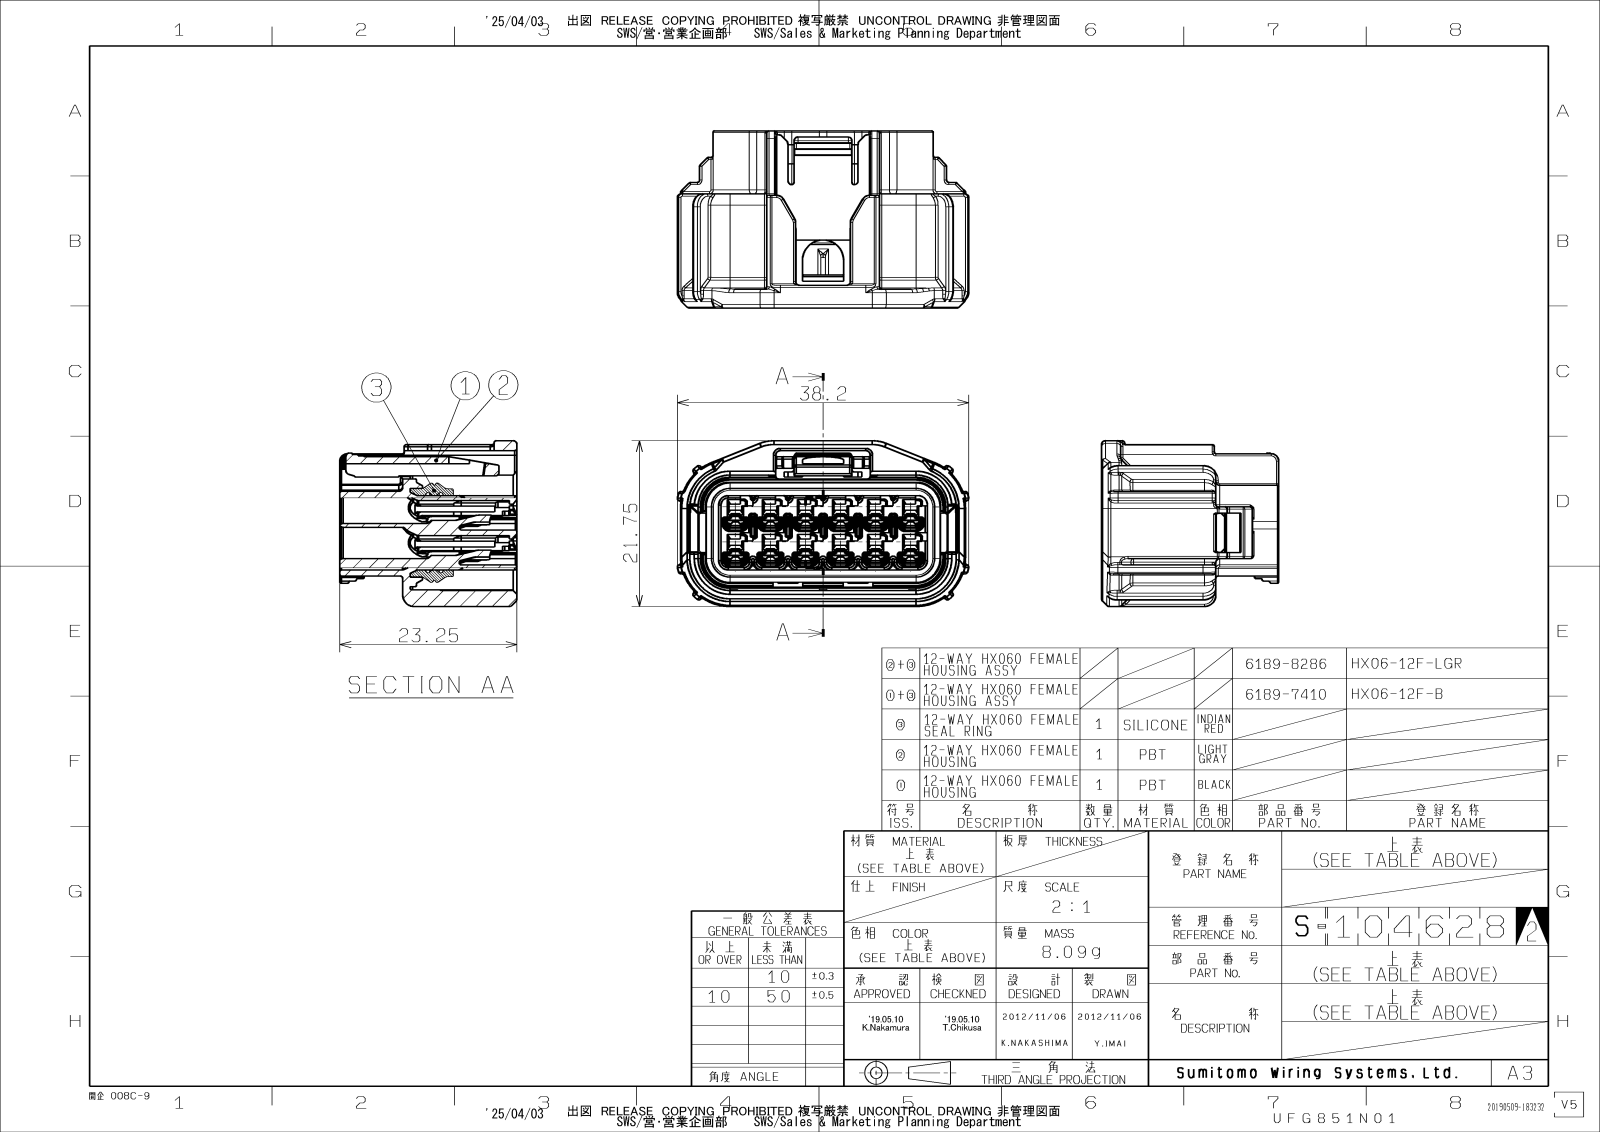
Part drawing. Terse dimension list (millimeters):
name: 6189-7410
written by: CATIA V5 STEP AP214 v2 (AUTOMOTIVE_DESIGN)
unit: mm
bodies: 1 solid, 442 faces (302 planar, 106 cylindrical, 34 other)
size: 38.2 × 23.25 × 21.75
volume: 8 858 mm³; area: 7 856 mm²
holes: 12× ⌀4.1
rounds: 12× R2.95, 7× R1, 7× R1.5, 6× R5, 4× R1.25, 4× R3.7, 4× R4.2, 4× R6.5
face distances: 2.7, 12.45, 0.8, 3.5, 1.2, 9.75, 13.25, 15, 15.95, 24.9
hole spacings: 4.6, 6.51, 9.2, 10.29, 13.8, 14.55, 18.4, 18.97
